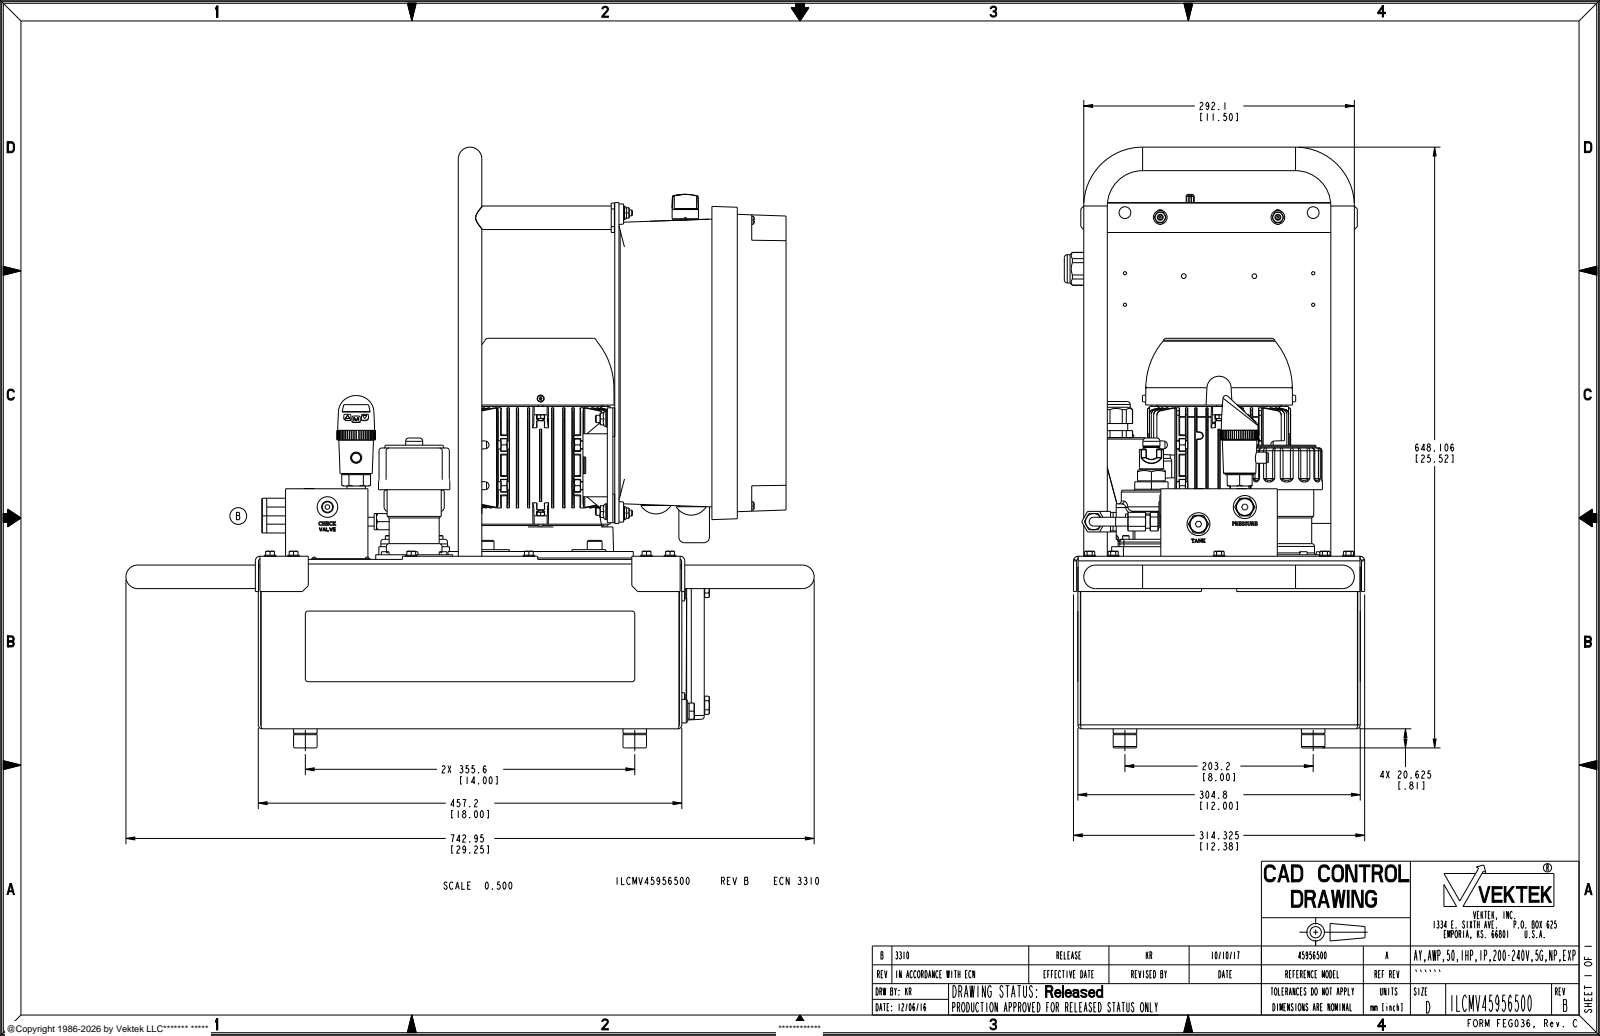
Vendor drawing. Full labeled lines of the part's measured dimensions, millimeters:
Part name (STEP PRODUCT): ILCMV45956500
STEP written by: PRO/ENGINEER BY PARAMETRIC TECHNOLOGY CORPORATION, 2013320 (AUTOMOTIVE_DESIGN)
Units: millimetres
Bodies: 20 solids, 10008 faces (4898 planar, 2411 cylindrical, 2699 other)
Overall size (bounding box): 742.95 × 648.11 × 324.21
Volume: 10 620 000 mm³ · Surface area: 3 320 000 mm²
Round holes (diameter × count): ⌀7.92 ×14, ⌀8.74 ×14, ⌀9.53 ×14, ⌀3.45 ×13, ⌀6 ×11, ⌀19.05 ×9, ⌀3 ×8, ⌀11.99 ×8, ⌀5.51 ×6, ⌀5.54 ×6, ⌀5.99 ×6, ⌀8.99 ×6
Round bosses / shafts (diameter × count): ⌀6.35 ×24, ⌀25.4 ×14, ⌀12.7 ×14, ⌀5 ×14, ⌀9.53 ×9, ⌀8.89 ×8, ⌀4.5 ×8, ⌀14.83 ×6
Partial cylindrical surfaces — rounded edges, fillets, slot ends (radius × count): R0.5 ×82, R2 ×61, R0.13 ×54, R1 ×53, R3 ×42, R4 ×28, R2.75 ×18, R1.52 ×14
Main face-to-face distances: 2.66, 3.5, 302.13, 454.53, 184.9, 179.32, 176.66, 2.74, 182.16, 299.47
Hole centre spacings: 2.5, 203.2, 3.54, 14.38, 59.49, 70, 82.49, 98.99
